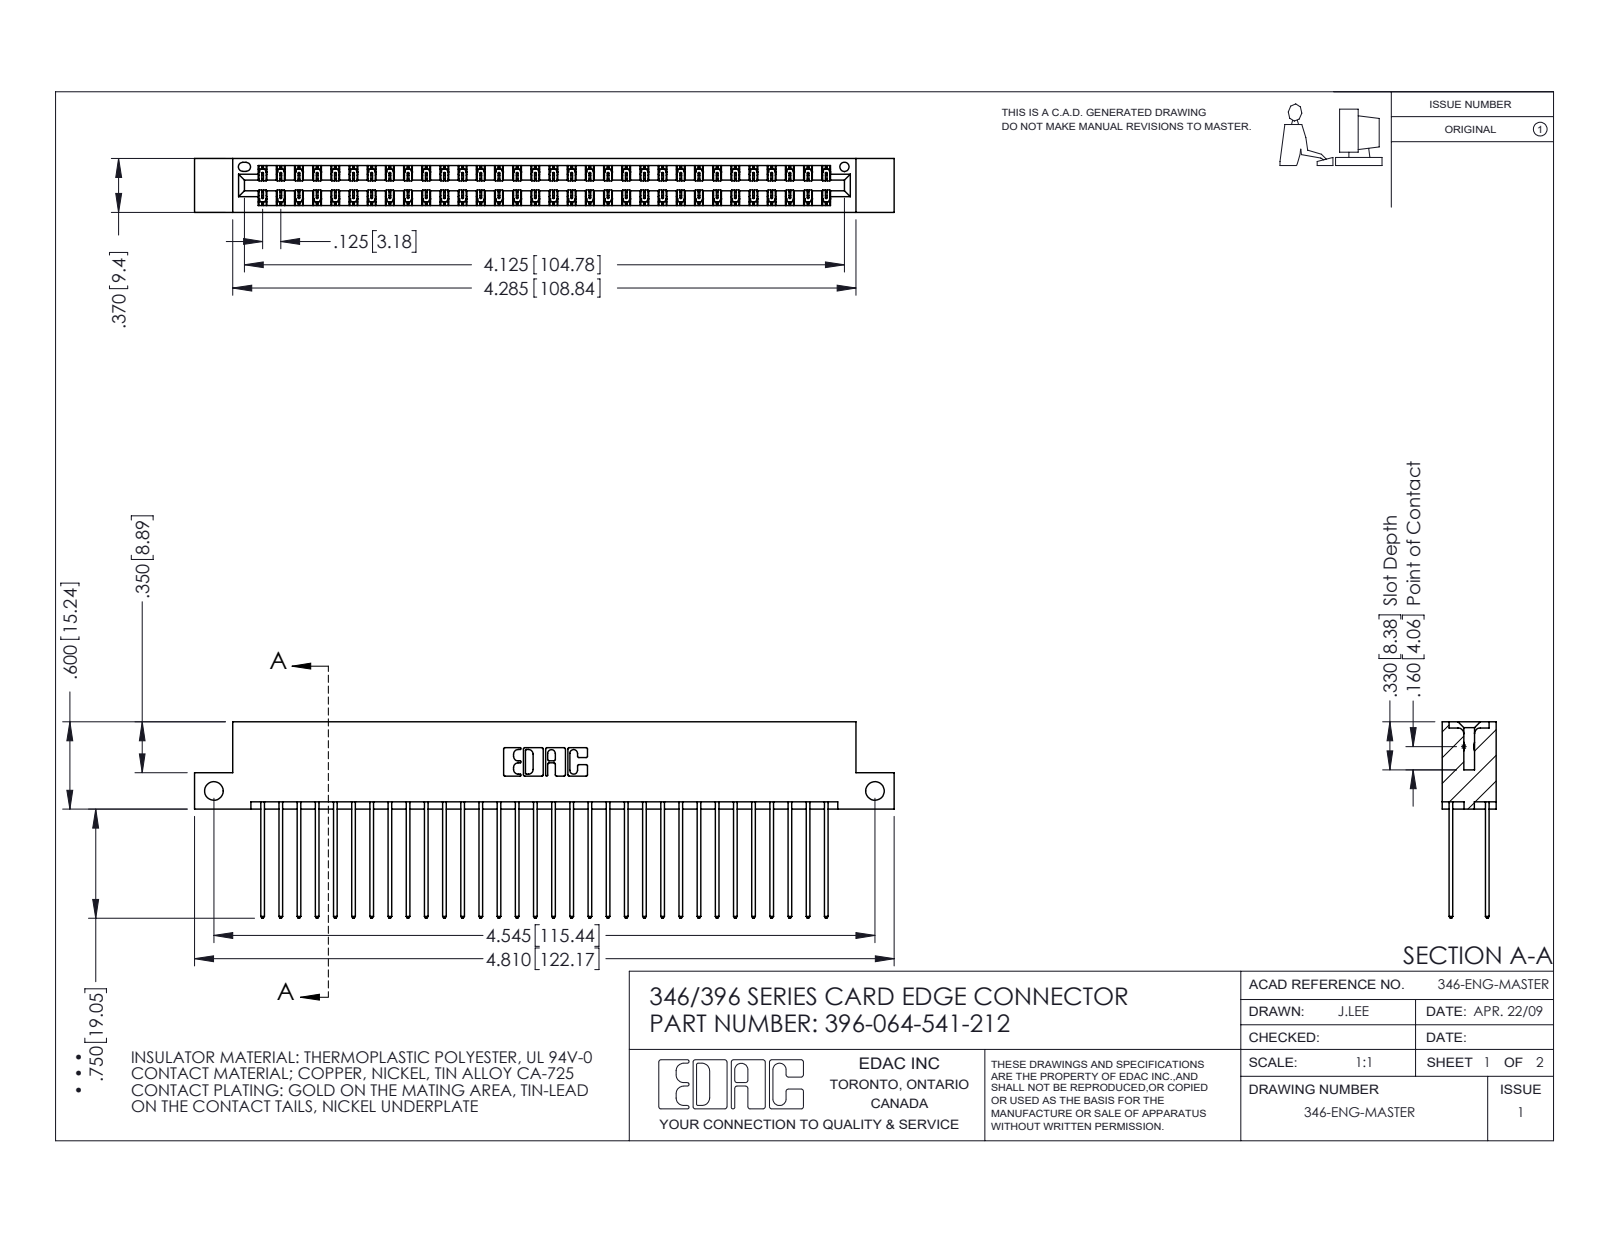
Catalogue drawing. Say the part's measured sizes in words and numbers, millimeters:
The part is named "396-064-541-212; 346 Part_Flush Mounting Lugs - Side Mount; 345-292-001_345-293-141". Its 3-D file was written by "SolidWorks 2016 (CONFIG_CONTROL_DESIGN)". It is 65 solids with 3450 faces: 2316 planar, 1134 cylindrical and 0 other. Overall it measures 122.2 by 34.3 by 9.4 millimeters. Its volume is 12 100 cubic millimeters and its surface area 18 120 square millimeters. Round holes: 2 of diameter 3.3, 1 of diameter 1.6. Partial cylindrical surfaces (rounded edges, fillets, slot ends): 96 of radius 0.2, 64 of radius 0.3, 22 of radius 0.3, 6 of radius 0.2, 6 of radius 0.8, 3 of radius 0.7, 2 of radius 0.4, 2 of radius 0.6. The main face-to-face distances are 1.2, 8.2, 6.4, 1.8, 7.6, 0.6, 9.4, 7, 5.7, 3.8. The hole center spacings are 115.4.
